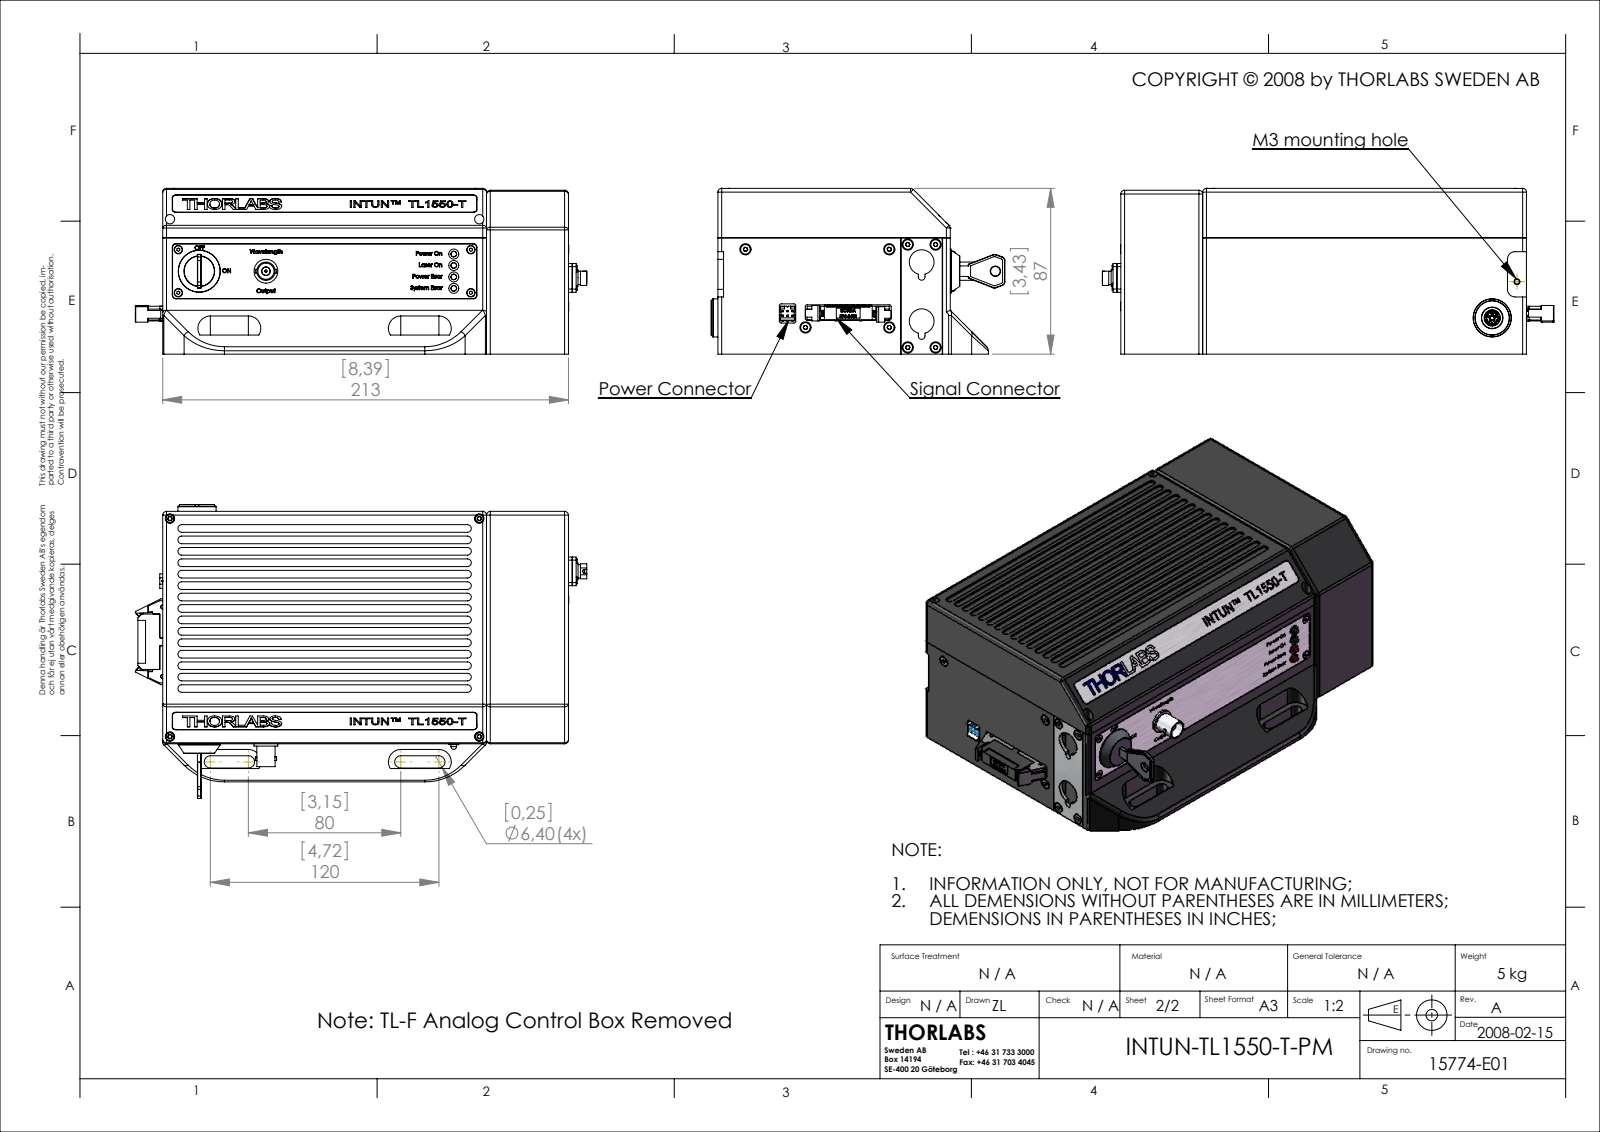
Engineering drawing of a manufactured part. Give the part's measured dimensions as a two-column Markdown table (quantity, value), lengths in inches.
| quantity | value |
| --- | --- |
| part name | INTUN-TL1550-T-PM |
| STEP written by | SolidWorks 2007 (CONFIG_CONTROL_DESIGN) |
| units | inches |
| bodies | 0 solids, 7651 faces (5117 planar, 1286 cylindrical, 1248 other) |
| overall size | 12.386 × 6.071 × 4.343 |
| round holes (diameter × count) | 0.039 × 33, 0.106 × 17, 0.063 × 12, 0.081 × 12, 0.094 × 12, 0.114 × 8, 0.193 × 8, 0.087 × 6, 0.433 × 6, 0.118 × 5, 0.169 × 5, 0.177 × 5 |
| round bosses / shafts (diameter × count) | 0.079 × 13, 0.098 × 12, 0.177 × 8, 0.157 × 8, 0.224 × 6, 0.209 × 6, 0.118 × 6, 0.866 × 5 |
| partial cylindrical surfaces (radius × count) | 0.079 × 100, 0.197 × 41, 0.006 × 20, 0.039 × 20, 0.071 × 16, 0.008 × 14, 0.039 × 12, 0.236 × 12 |
| main face-to-face distances | 0.197, 0.039, 0.079, 0.118, 0.236, 0.246, 3.425, 3.386, 3.189, 0.157 |
| hole center spacings | 0.126, 0.136, 0.191, 0.25, 0.374, 0.876, 0.876, 0.071 |
